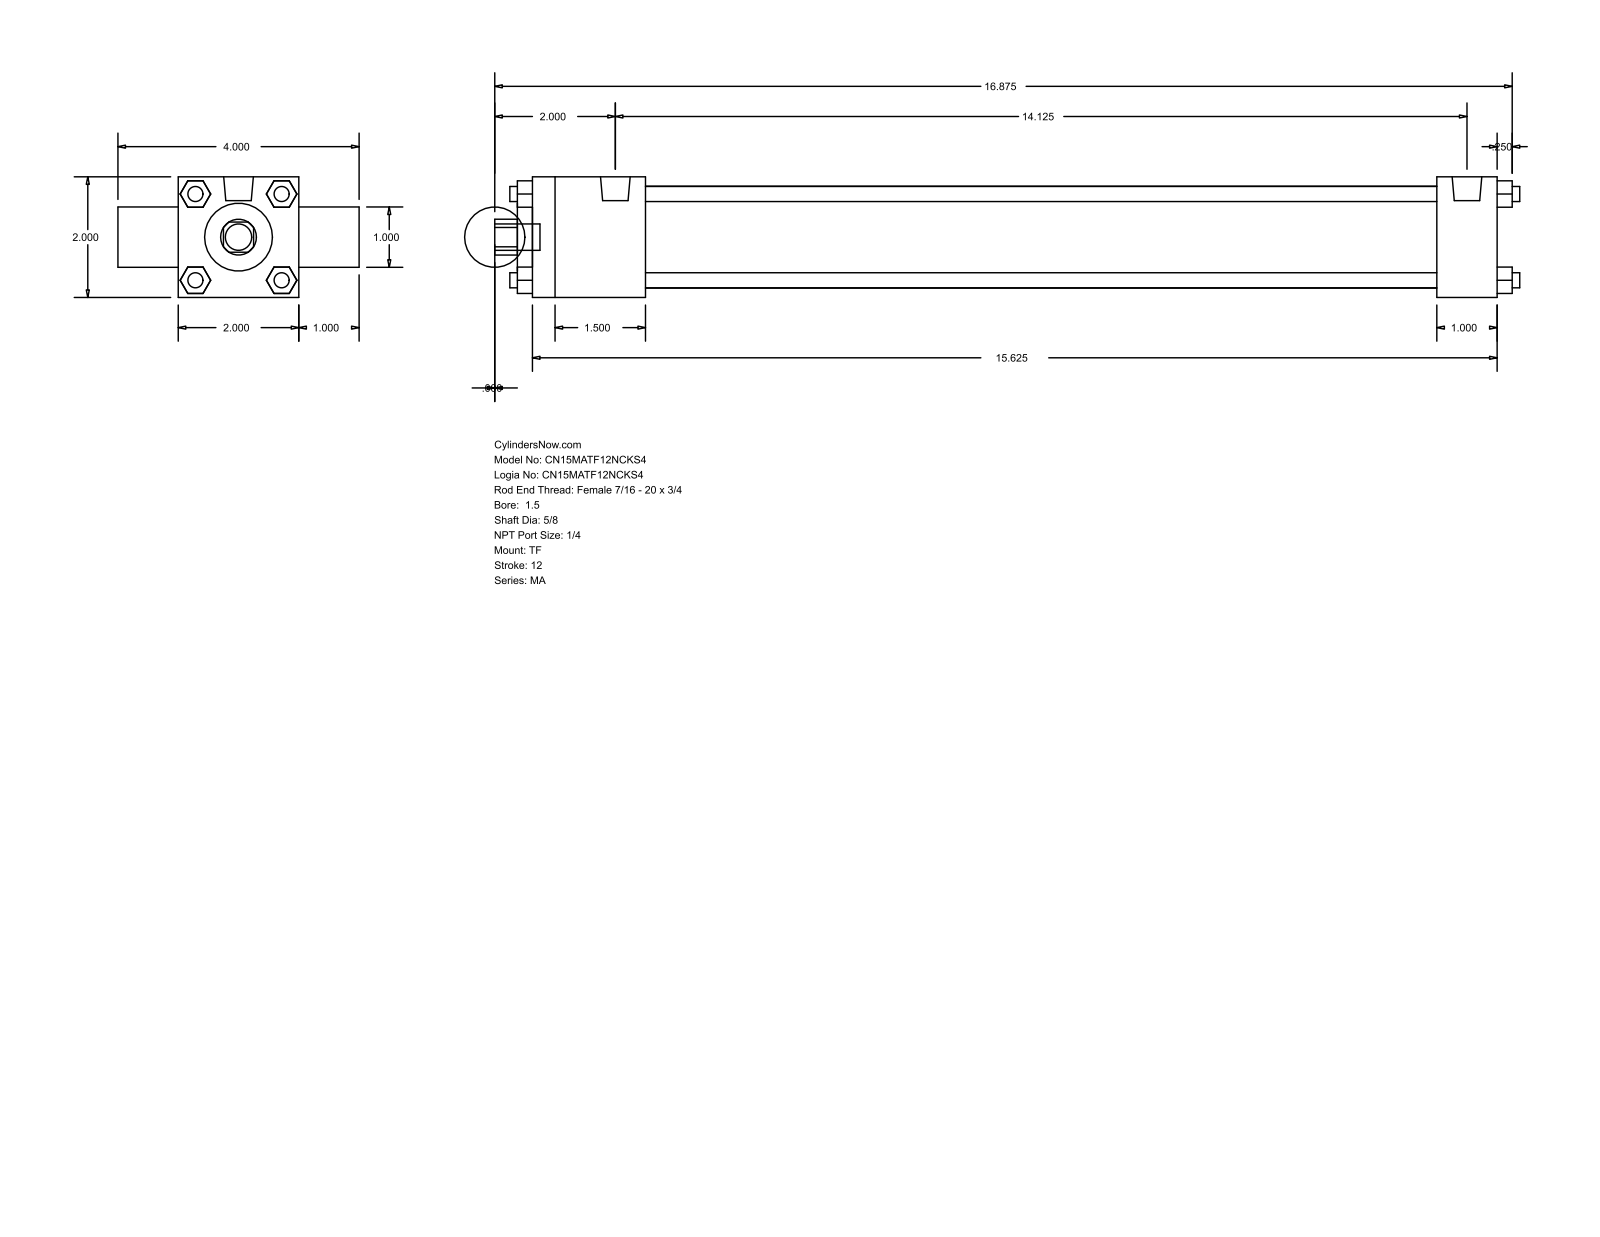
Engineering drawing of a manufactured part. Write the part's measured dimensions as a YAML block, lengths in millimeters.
part_name: "MA_TF__0150_0.625"
step_written_by: "GSSL Pune (CONFIG_CONTROL_DESIGN)"
units: millimeters
bodies: {solids: 0, faces: 120, planar: 92, cylindrical: 28, other: 0}
overall_size: [431.8, 101.6, 50.8]
round_holes:
  - {diameter: 15.88, count: 1}
  - {diameter: 25.4, count: 1}
  - {diameter: 28.57, count: 1}
  - {diameter: 42.93, count: 1}
round_bosses_or_shafts:
  - {diameter: 6.35, count: 4}
  - {diameter: 7.94, count: 3}
  - {diameter: 12.49, count: 2}
  - {diameter: 11.11, count: 1}
partial_cylinders:
  - {radius: 7.54, count: 1}
face_to_face_distances: [50.8, 406.39, 6.35, 412.74, 25.4, 76.2, 47.62, 381, 333.38, 358.77]
